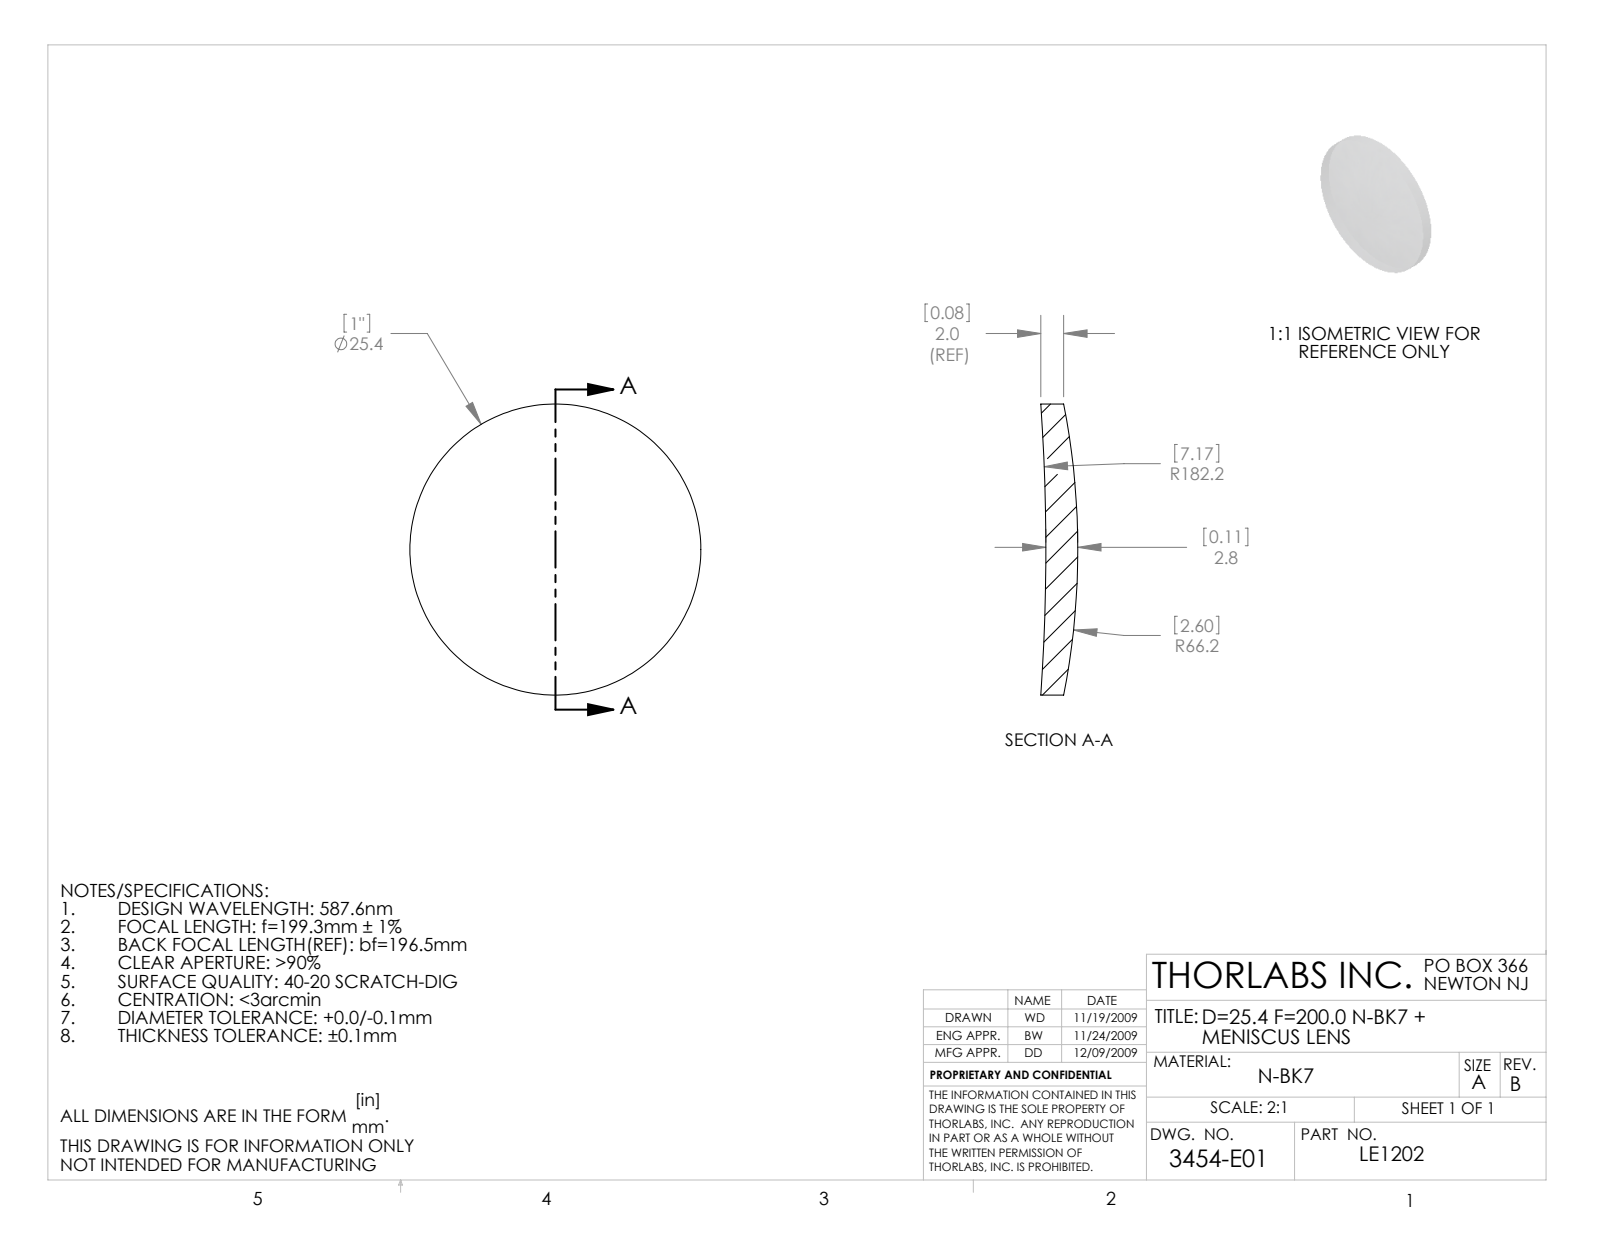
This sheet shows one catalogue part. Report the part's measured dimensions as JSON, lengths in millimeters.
{"part_name": "3454-E0W", "step_written_by": "SolidWorks 2009 (AUTOMOTIVE_DESIGN)", "units": "millimeters", "bodies": {"solids": 1, "faces": 6, "planar": 0, "cylindrical": 2, "other": 4}, "overall_size": [25.4, 25.4, 3.23], "volume_mm3": 1215, "surface_area_mm2": 1179, "round_bosses_or_shafts": [[25.4, 1]]}
